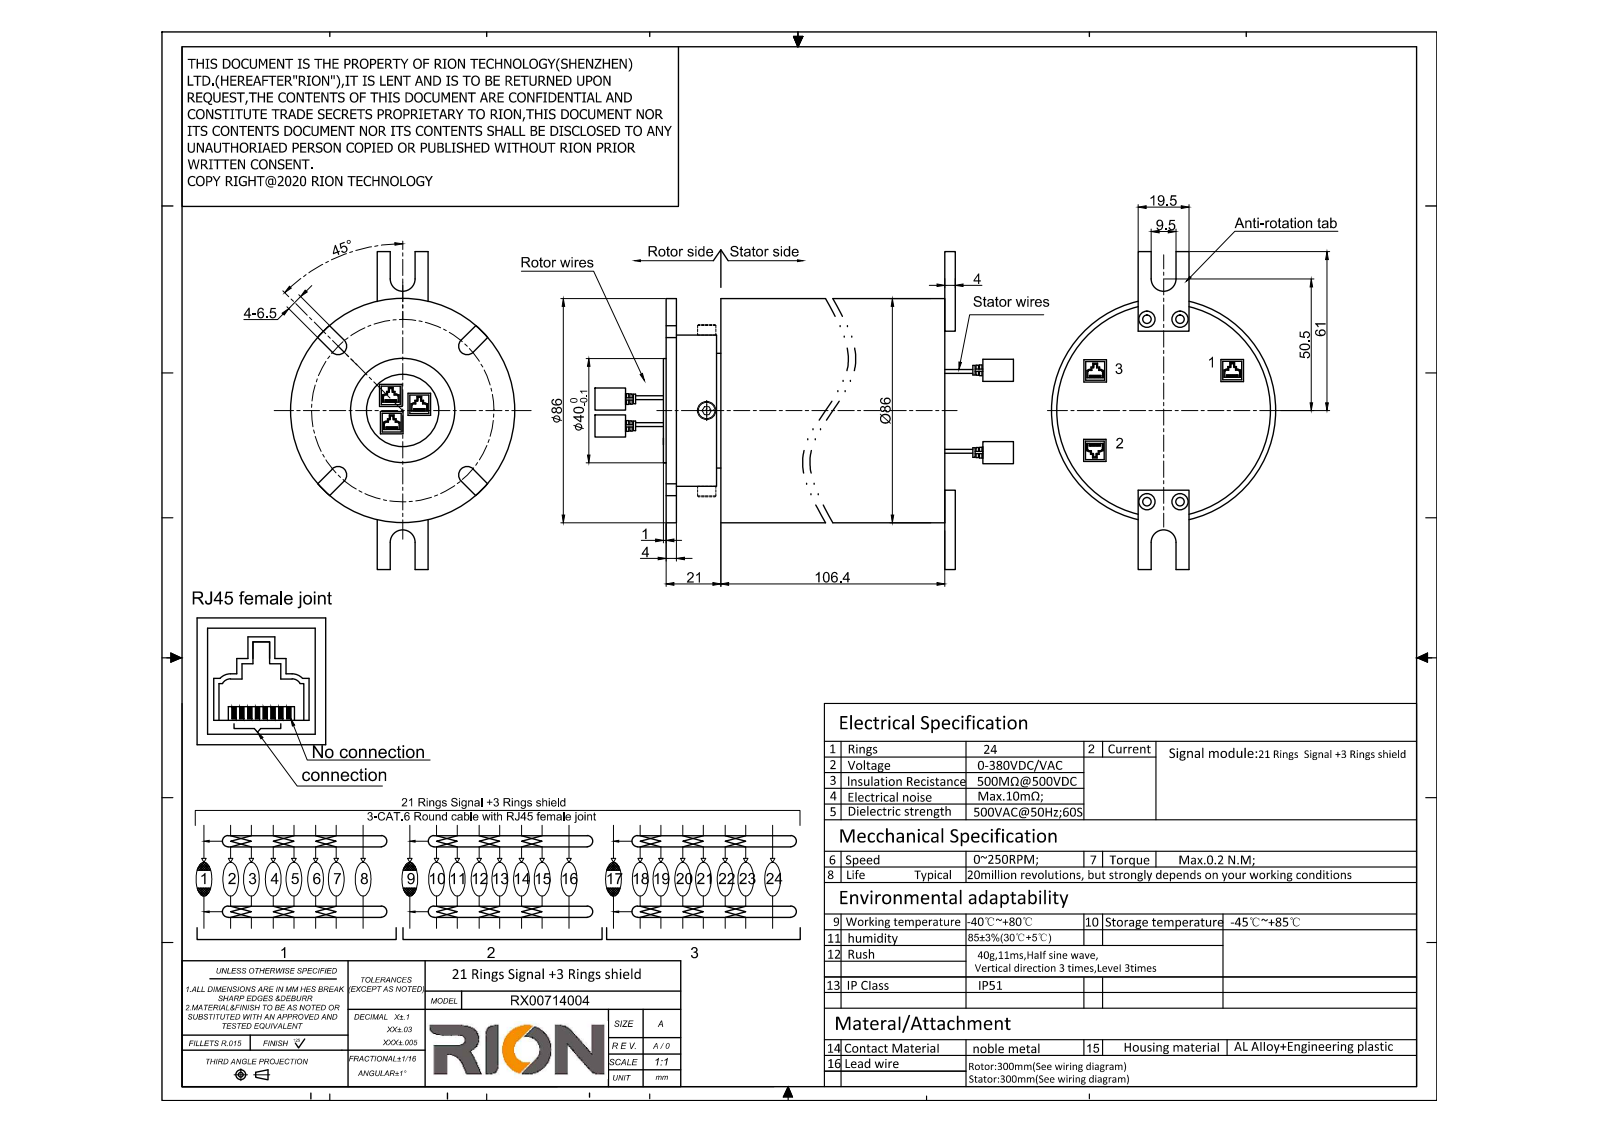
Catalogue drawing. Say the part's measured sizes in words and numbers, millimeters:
The part is named "RX00714004". Its 3-D file was written by "SolidWorks 2014 (CONFIG_CONTROL_DESIGN)". It is 1 solid with 98 faces: 39 planar, 43 cylindrical and 16 other. Overall it measures 167.4 by 122 by 86 millimeters. Its volume is 690 591 cubic millimeters and its surface area 57 500 square millimeters. Round holes: 4 of diameter 3.2, 1 of diameter 30.11. Round bosses or shafts: 6 of diameter 6, 1 of diameter 86, 1 of diameter 58, 1 of diameter 44, 1 of diameter 40. Partial cylindrical surfaces (rounded edges, fillets, slot ends): 4 of radius 3.25, 2 of radius 4.75. The main face-to-face distances are 127.4, 106.4, 21, 4, 123.4, 17, 108, 1.6, 15.4, 19.4. The hole center spacings are 35.57, 12.7, 70, 71.14.
